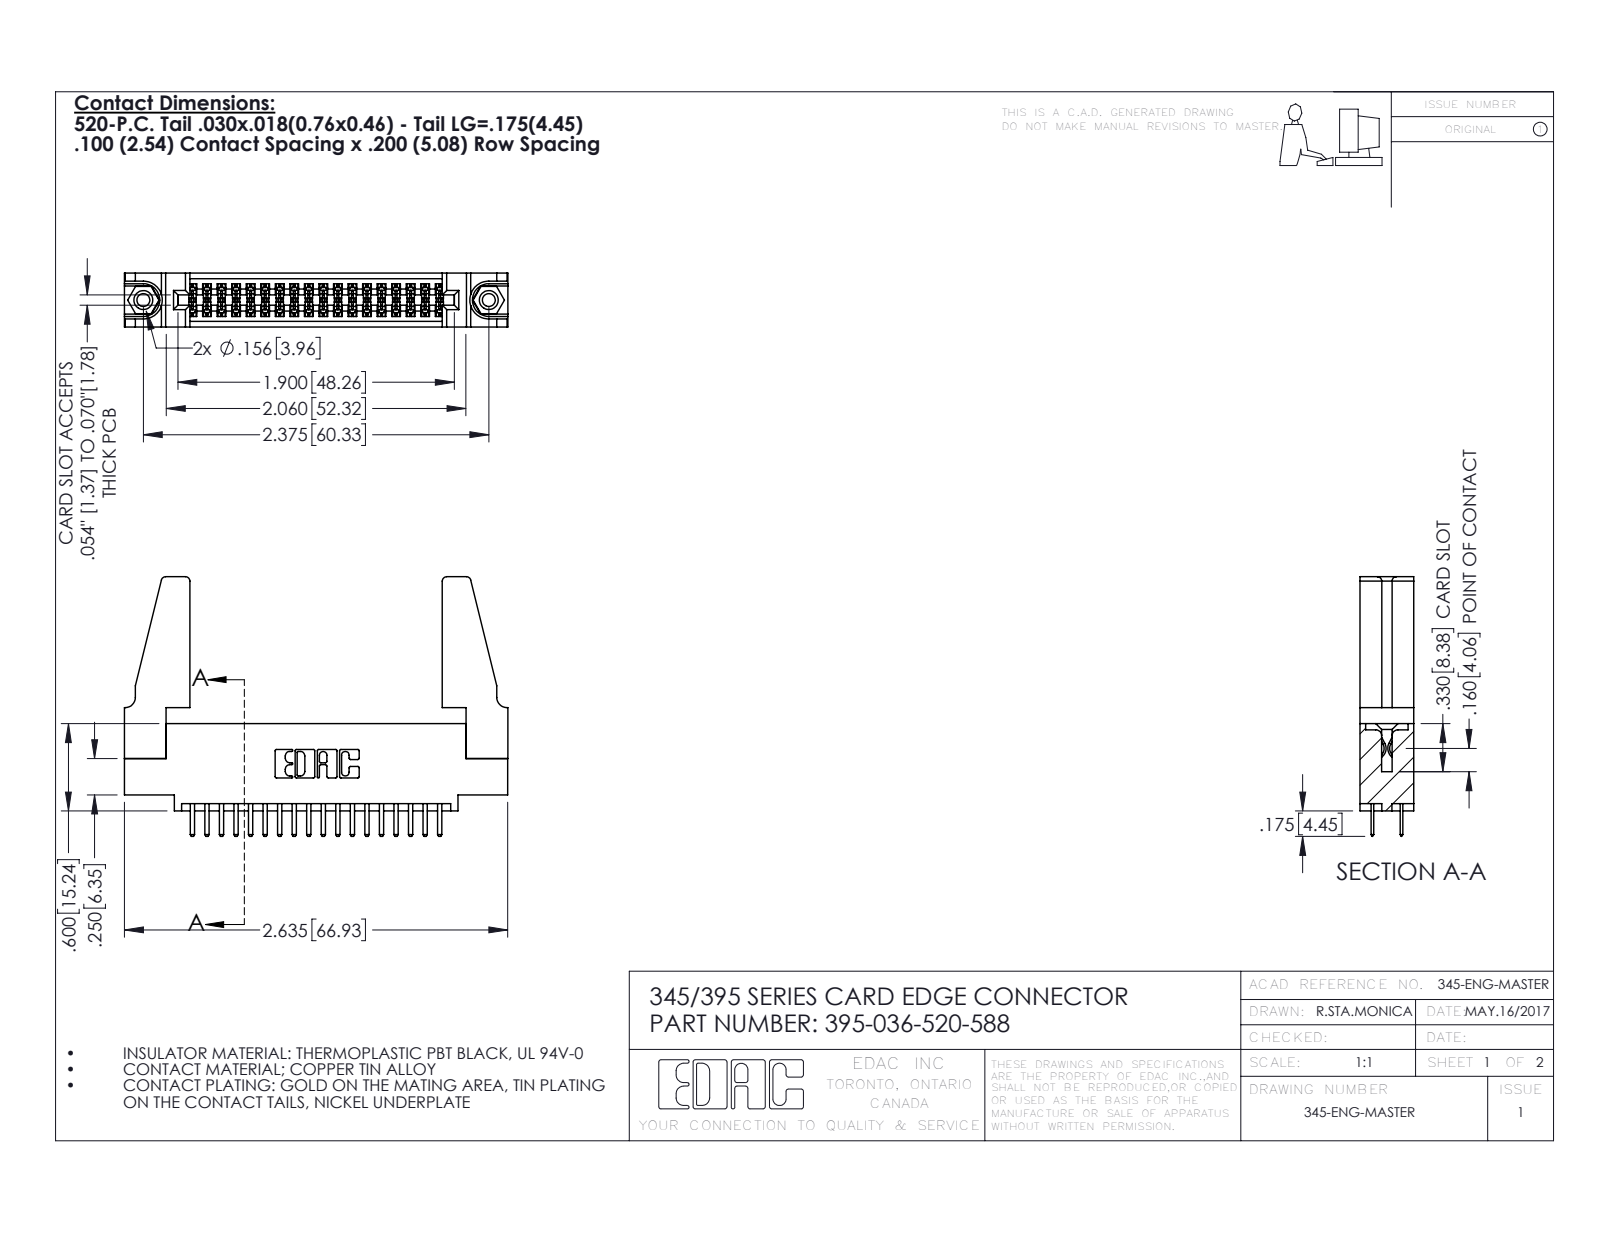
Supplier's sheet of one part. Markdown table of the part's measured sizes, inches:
| quantity | value |
| --- | --- |
| part name | 395-036-520-588; 345-292-001_345-293-120; 345-250-001_345-250-001-102; 345 Part_0.110 Offset - 0.156 Dia-TH (+1 more) |
| STEP written by | SolidWorks 2016 (CONFIG_CONTROL_DESIGN) |
| units | inches |
| bodies | 41 solids, 2198 faces (1416 planar, 766 cylindrical, 16 other) |
| overall size | 2.636 × 1.785 × 0.37 |
| volume | 0.576 in³ |
| surface area | 18.4 in² |
| round holes (diameter × count) | 0.089 × 2, 0.125 × 2, 0.156 × 2, 0.064 × 1 |
| round bosses / shafts (diameter × count) | 0.155 × 2 |
| partial cylindrical surfaces (radius × count) | 0.006 × 54, 0.01 × 40, 0.01 × 22, 0.03 × 8, 0.007 × 6, 0.031 × 6, 0.026 × 3, 0.014 × 2 |
| main face-to-face distances | 0.37, 0.072, 0.298, 0.2, 0.098, 0.272, 0.025, 0.225, 0.072, 0.022 |
| hole center spacings | 0.27, 2.141, 2.375 |
